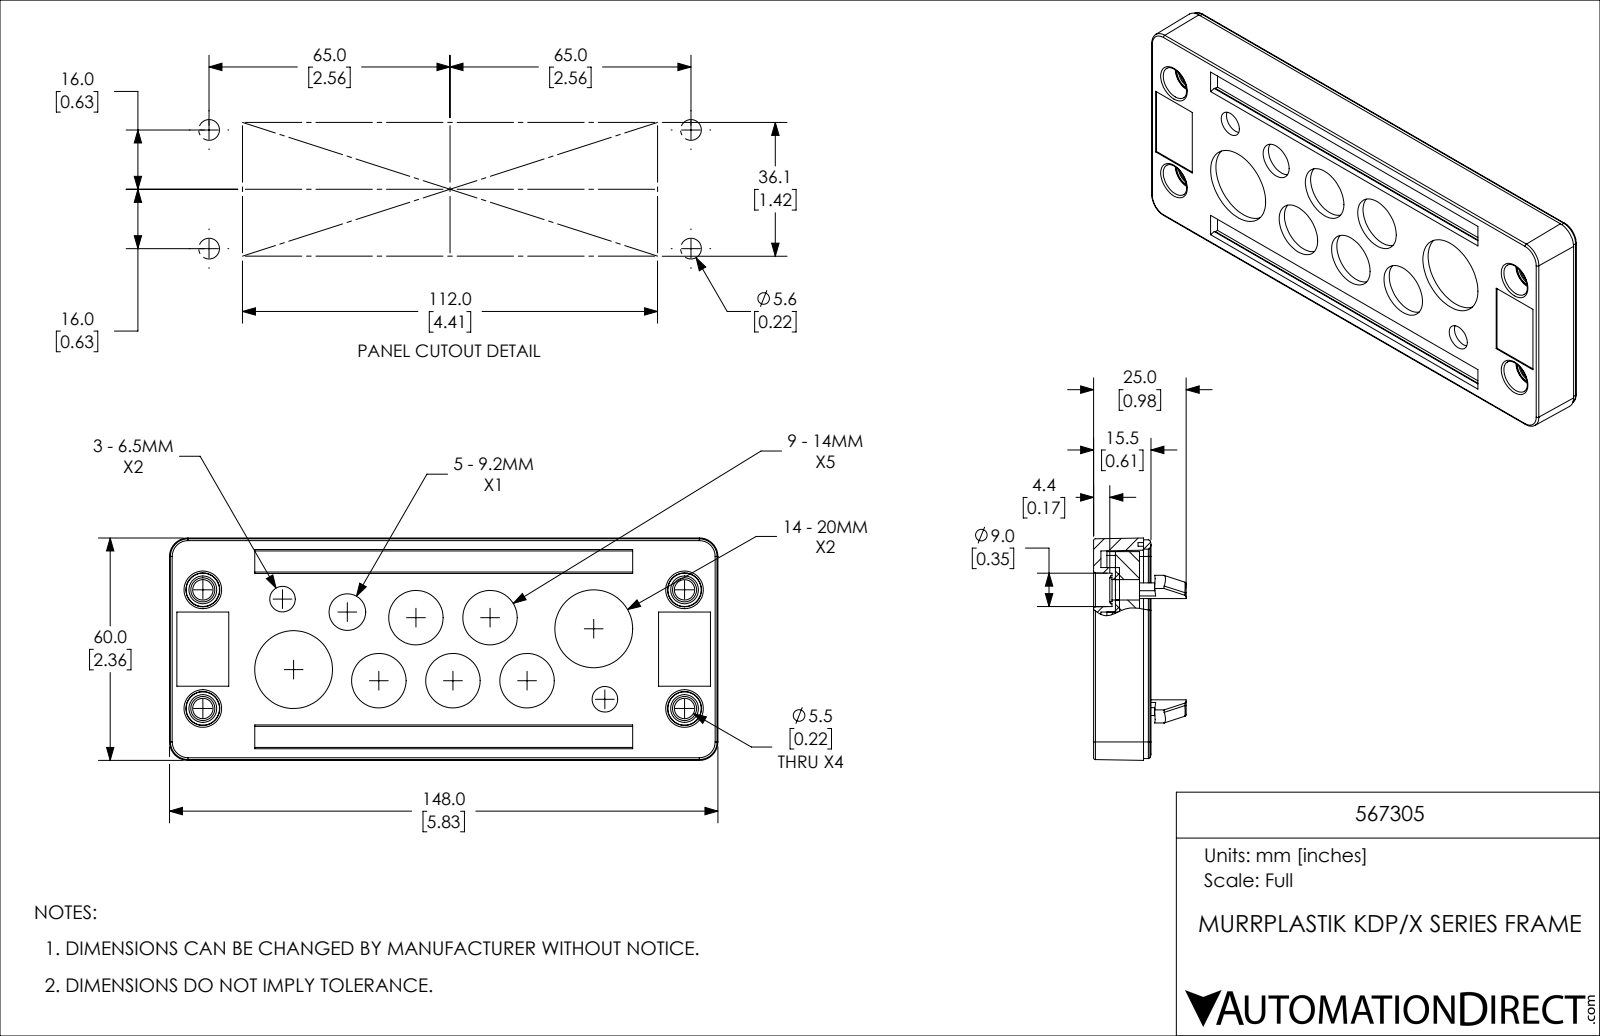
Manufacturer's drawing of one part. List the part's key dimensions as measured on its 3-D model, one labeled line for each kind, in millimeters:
Part name (STEP PRODUCT): 567305
STEP written by: SolidWorks 2019 (CONFIG_CONTROL_DESIGN)
Units: millimetres
Bodies: 4 solids, 410 faces (178 planar, 180 cylindrical, 52 other)
Overall size (bounding box): 148 × 60 × 25
Volume: 76 209 mm³ · Surface area: 62 454 mm²
Round holes (diameter × count): ⌀14.7 ×5, ⌀19 ×5, ⌀5.5 ×4, ⌀6.5 ×4, ⌀6.9 ×2, ⌀11 ×2, ⌀21 ×2, ⌀25 ×2, ⌀9.9 ×1, ⌀13.8 ×1
Round bosses / shafts (diameter × count): ⌀7.5 ×4
Partial cylindrical surfaces — rounded edges, fillets, slot ends (radius × count): R0.5 ×16, R2 ×12, R1 ×8, R3 ×8, R2.75 ×4, R3.25 ×4, R3.5 ×4, R3.75 ×4
Main face-to-face distances: 2.3, 3.3, 6.5, 3.6, 5.9, 8.8, 12.4, 2, 1.6, 3.9
Hole centre spacings: 19.72, 20, 17.72, 5, 15, 34.48, 48.09, 22.67
